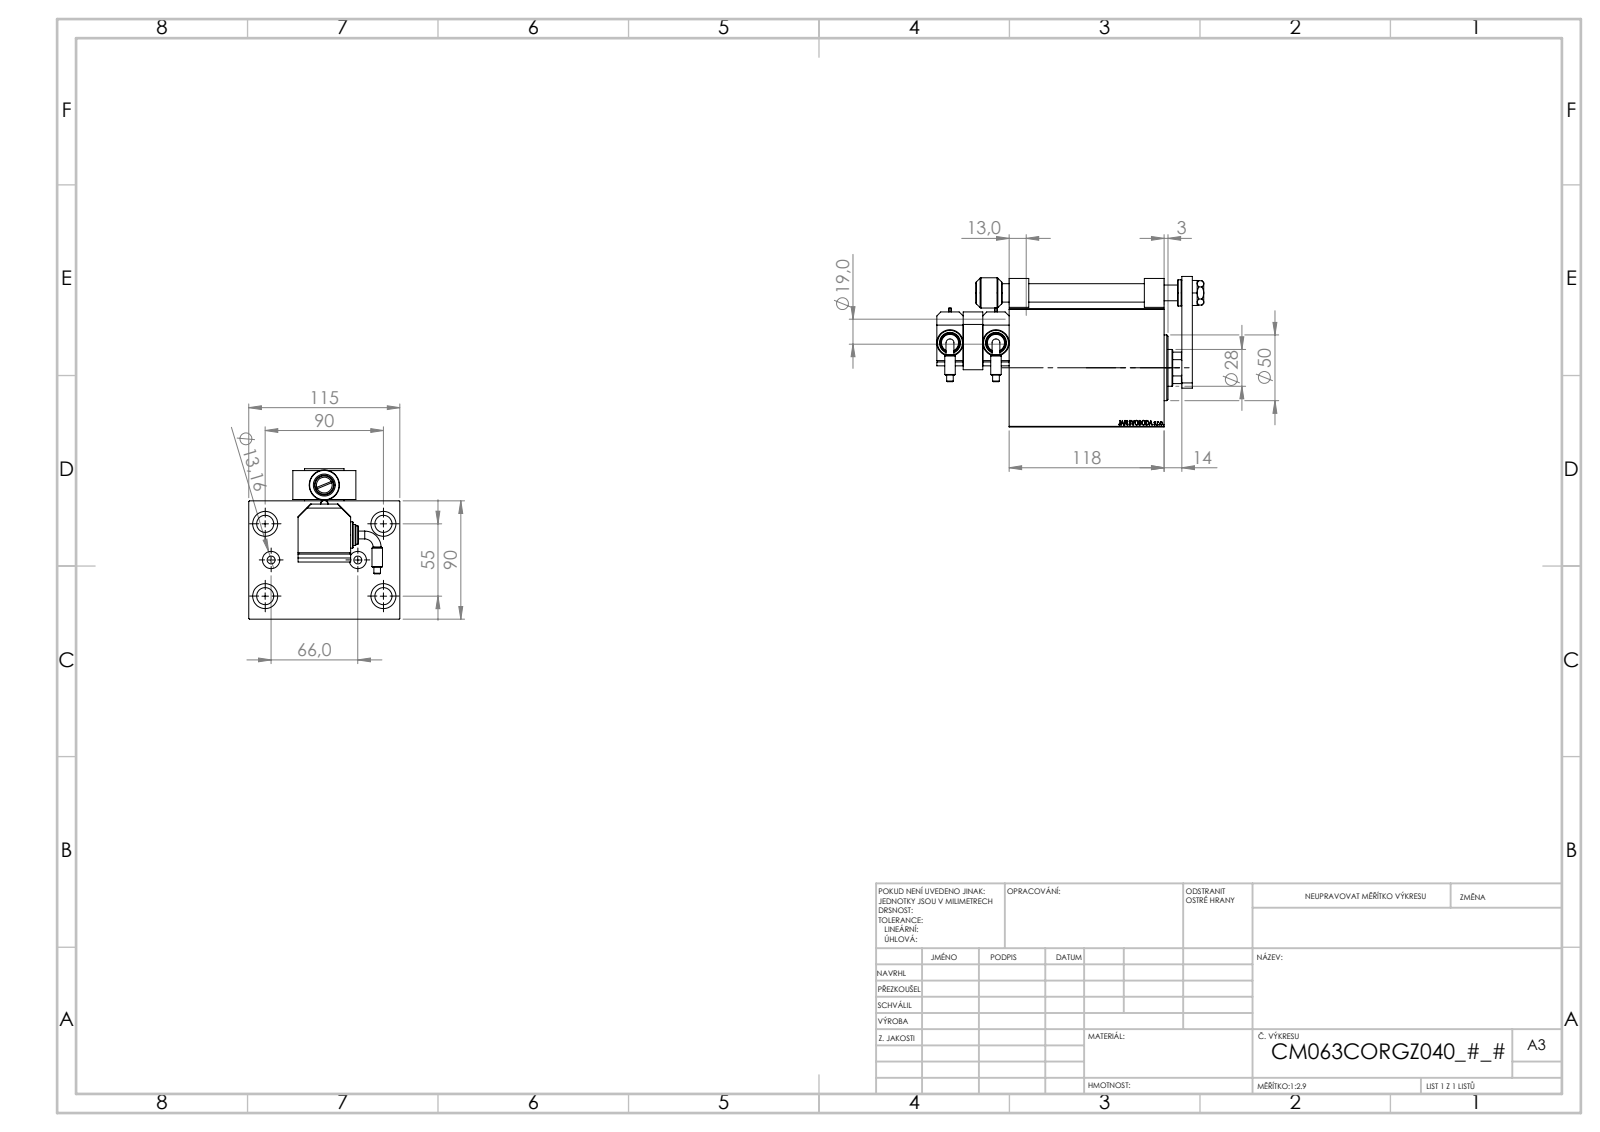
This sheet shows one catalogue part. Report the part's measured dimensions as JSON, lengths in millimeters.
{"part_name": "NUT_D16; V450CM_C_VCP; SWITCH P; SWITCH DIM W_B (+7 more)", "step_written_by": "SolidWorks 2019 (CONFIG_CONTROL_DESIGN)", "units": "millimeters", "bodies": {"solids": 14, "faces": 1114, "planar": 525, "cylindrical": 124, "other": 465}, "overall_size": [203.2, 115, 114.5], "volume_mm3": 1205000, "surface_area_mm2": 184608, "round_holes": [[13, 5], [4, 4], [8, 4], [19, 4], [6, 2], [13.16, 2], [12, 1], [14, 1], [16.5, 1], [18.5, 1], [28, 1], [31.5, 1]], "round_bosses_or_shafts": [[20, 3], [16, 2], [14, 2], [8, 2], [6, 2], [5.04, 2], [50, 1], [23, 1]], "partial_cylinders_radius": [[3, 1], [13.5, 1]], "face_to_face_distances": [90, 115, 118, 35, 46, 72, 5, 15, 20, 103], "hole_center_spacings": [30, 52.74, 82.71, 20, 33, 53.81, 55, 65.86]}
